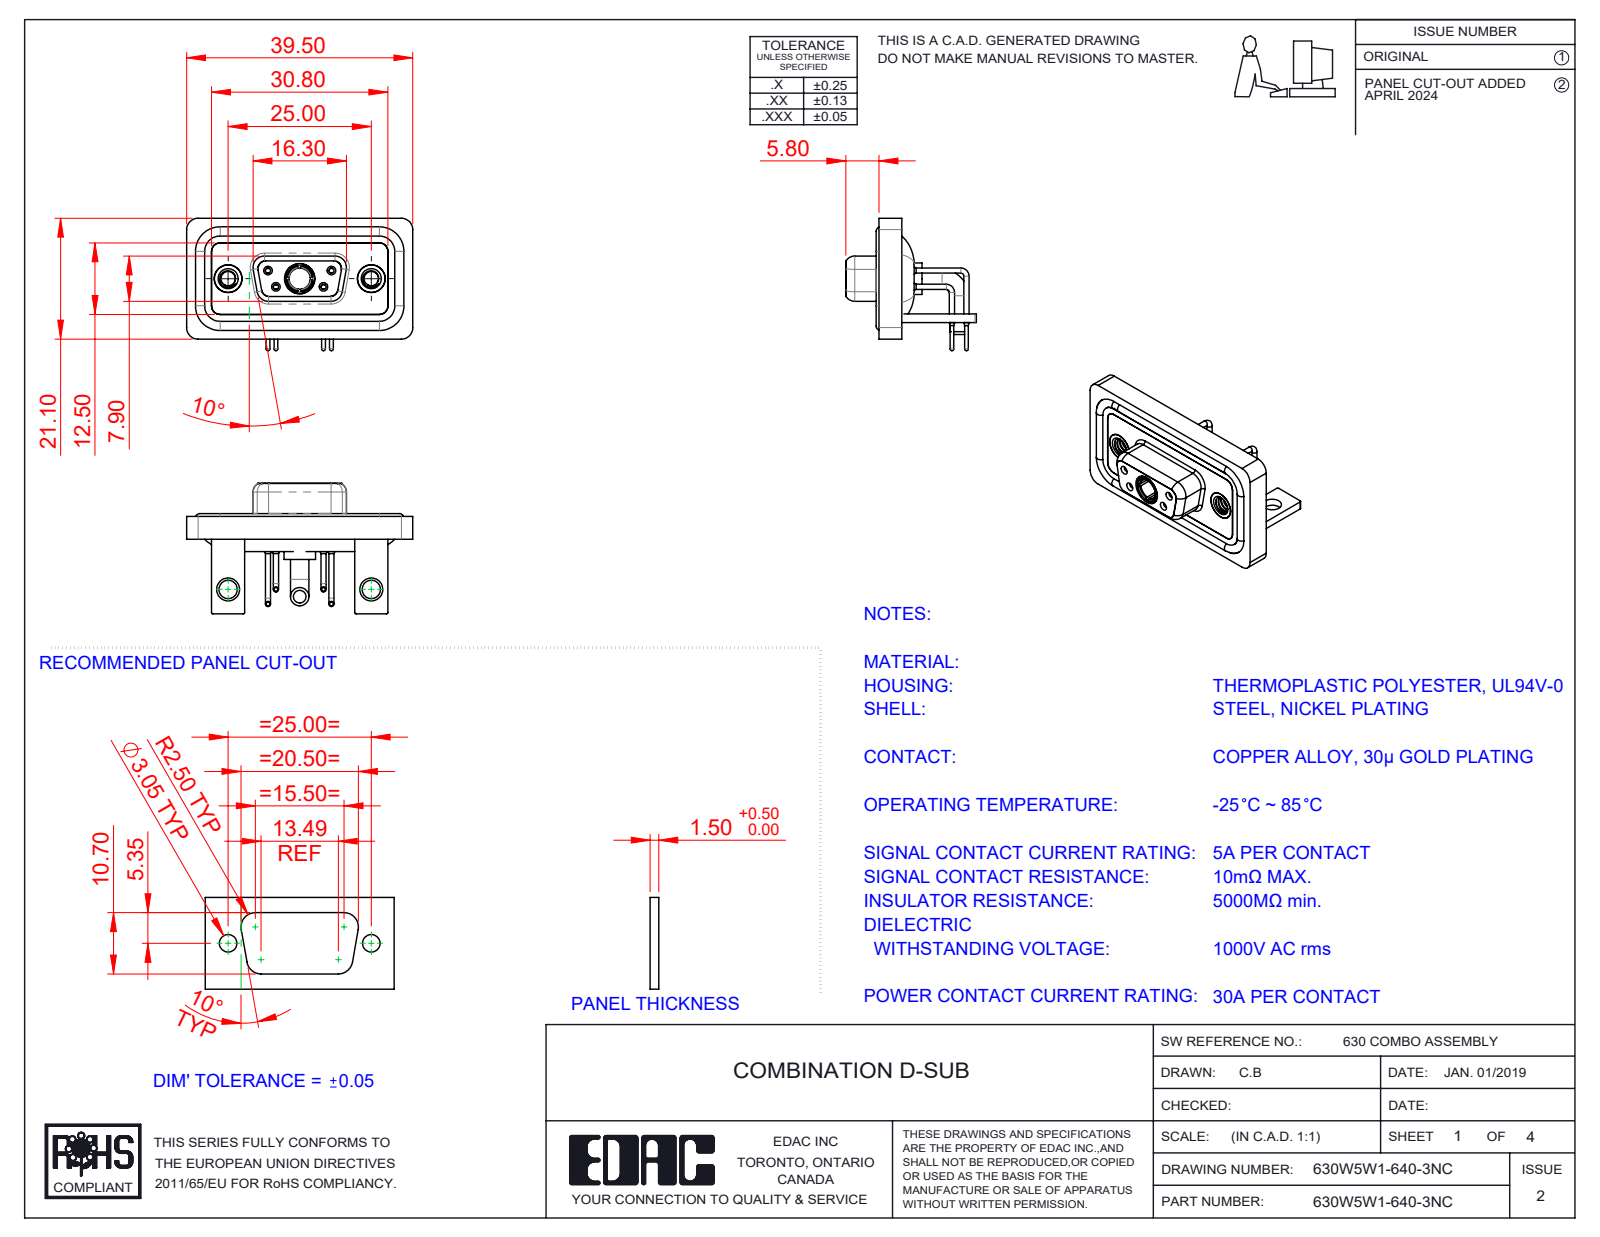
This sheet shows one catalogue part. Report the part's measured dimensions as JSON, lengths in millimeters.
{"part_name": "Power Socket_30A RA; 630Combo Stabilizer Bracket_50 Contacts; 630W5W1-640-3NC; 630Combo Contact Row 1_50 Contacts (+6 more)", "step_written_by": "SolidWorks 2023 (CONFIG_CONTROL_DESIGN)", "units": "millimeters", "bodies": {"solids": 15, "faces": 718, "planar": 214, "cylindrical": 327, "other": 177}, "overall_size": [39.5, 23.12, 22.8], "volume_mm3": 5216, "surface_area_mm2": 8600, "round_holes": [[0.9, 4], [1.1, 4], [1.5, 4], [2, 4], [4.85, 3], [1.6, 2], [1.7, 2], [2.5, 2], [3.2, 2], [4, 2], [4.05, 2], [5, 2]], "round_bosses_or_shafts": [[1.6, 6], [0.9, 4], [0.65, 4], [4.95, 2], [4.8, 2], [3.2, 2], [5.5, 1], [5.2, 1]], "partial_cylinders_radius": [[2, 19], [1.5, 18], [0.25, 16], [1.35, 8], [1.6, 8], [0.5, 5], [0.6, 4], [0.65, 4]], "face_to_face_distances": [0.4, 2.9, 1.5, 1.8, 1.1, 3.7, 1.6, 0.8, 2.5, 3.1], "hole_center_spacings": [3.16, 5.72, 7.1, 12.5, 18.1, 25, 4.39, 4.4]}
